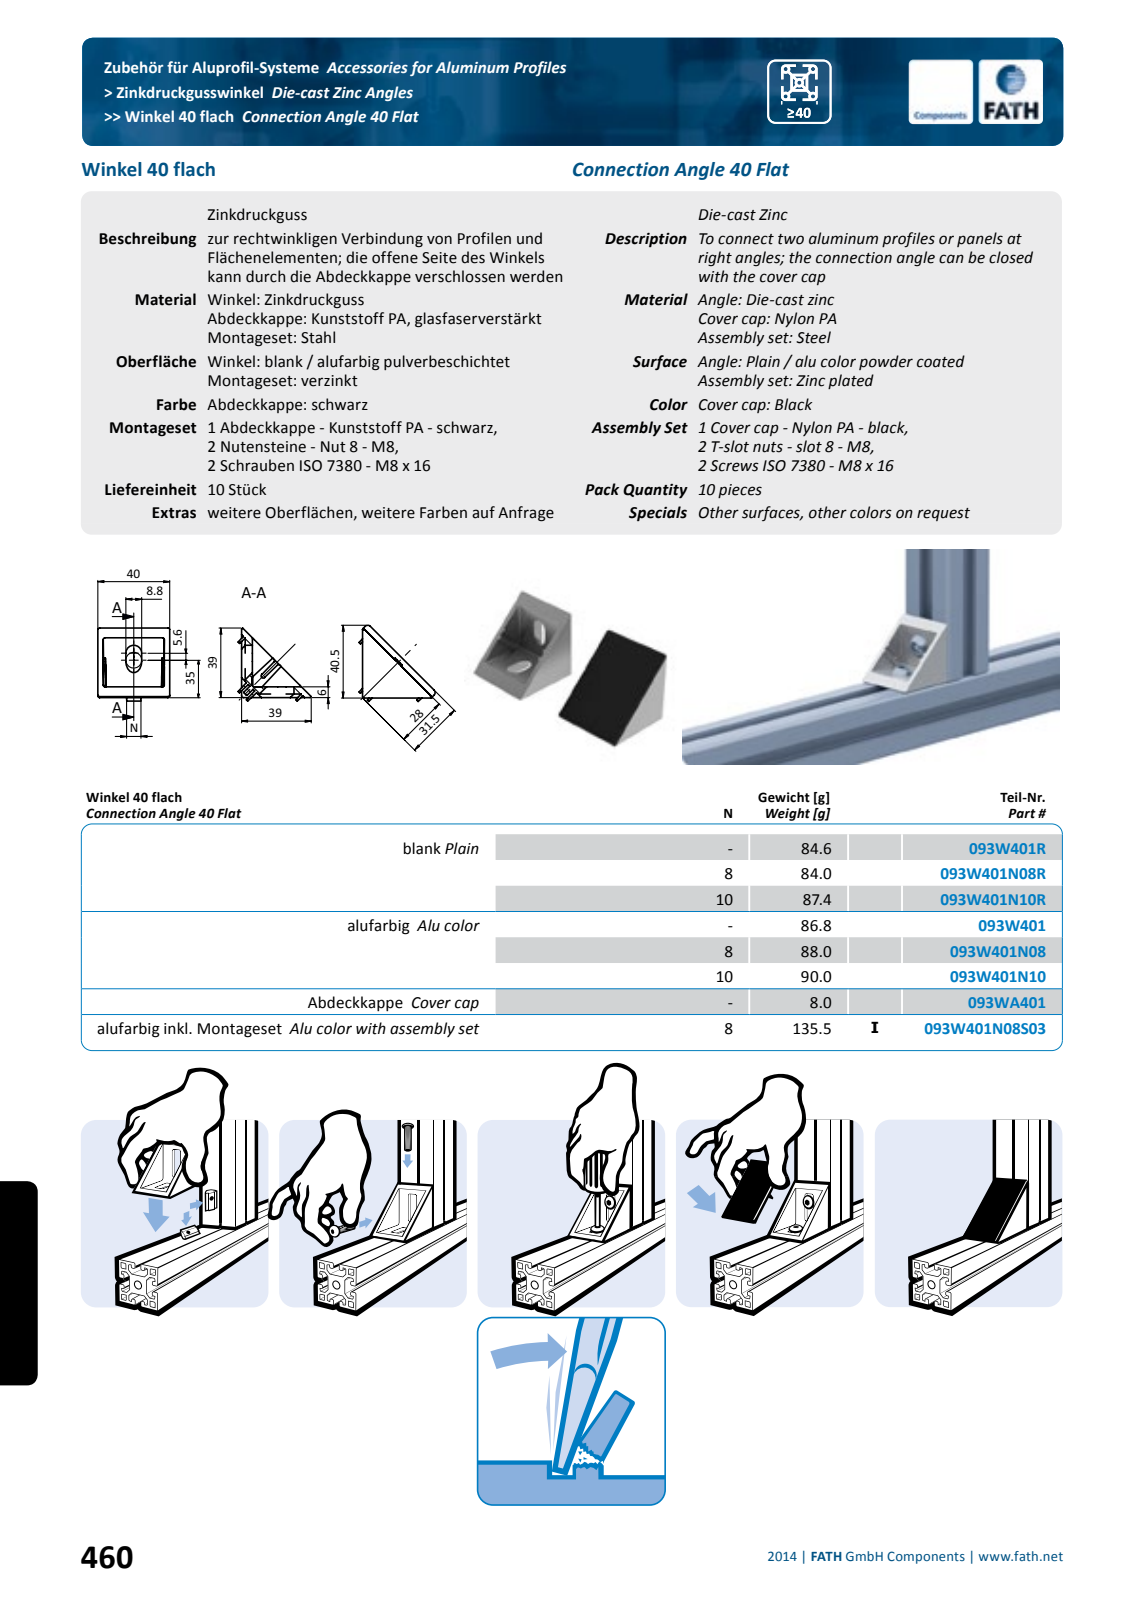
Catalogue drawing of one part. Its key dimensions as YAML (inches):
part_name: "fath_093w401n08r"
step_written_by: "Spatial InterOp 3D (automotive_design)"
units: inches
bodies: {solids: 1, faces: 171, planar: 112, cylindrical: 55, other: 4}
overall_size: [2.126, 1.575, 1.079]
volume: 0.807
surface_area: 14.71
round_bosses_or_shafts:
  - {diameter: 0.157, count: 4}
partial_cylinders:
  - {radius: 0.039, count: 34}
  - {radius: 0.173, count: 4}
  - {radius: 0.02, count: 2}
  - {radius: 0.046, count: 2}
face_to_face_distances: [0.236, 0.118, 0.118, 1.023, 0.047, 0.079, 0.157, 0.039, 0.083, 0.429]
